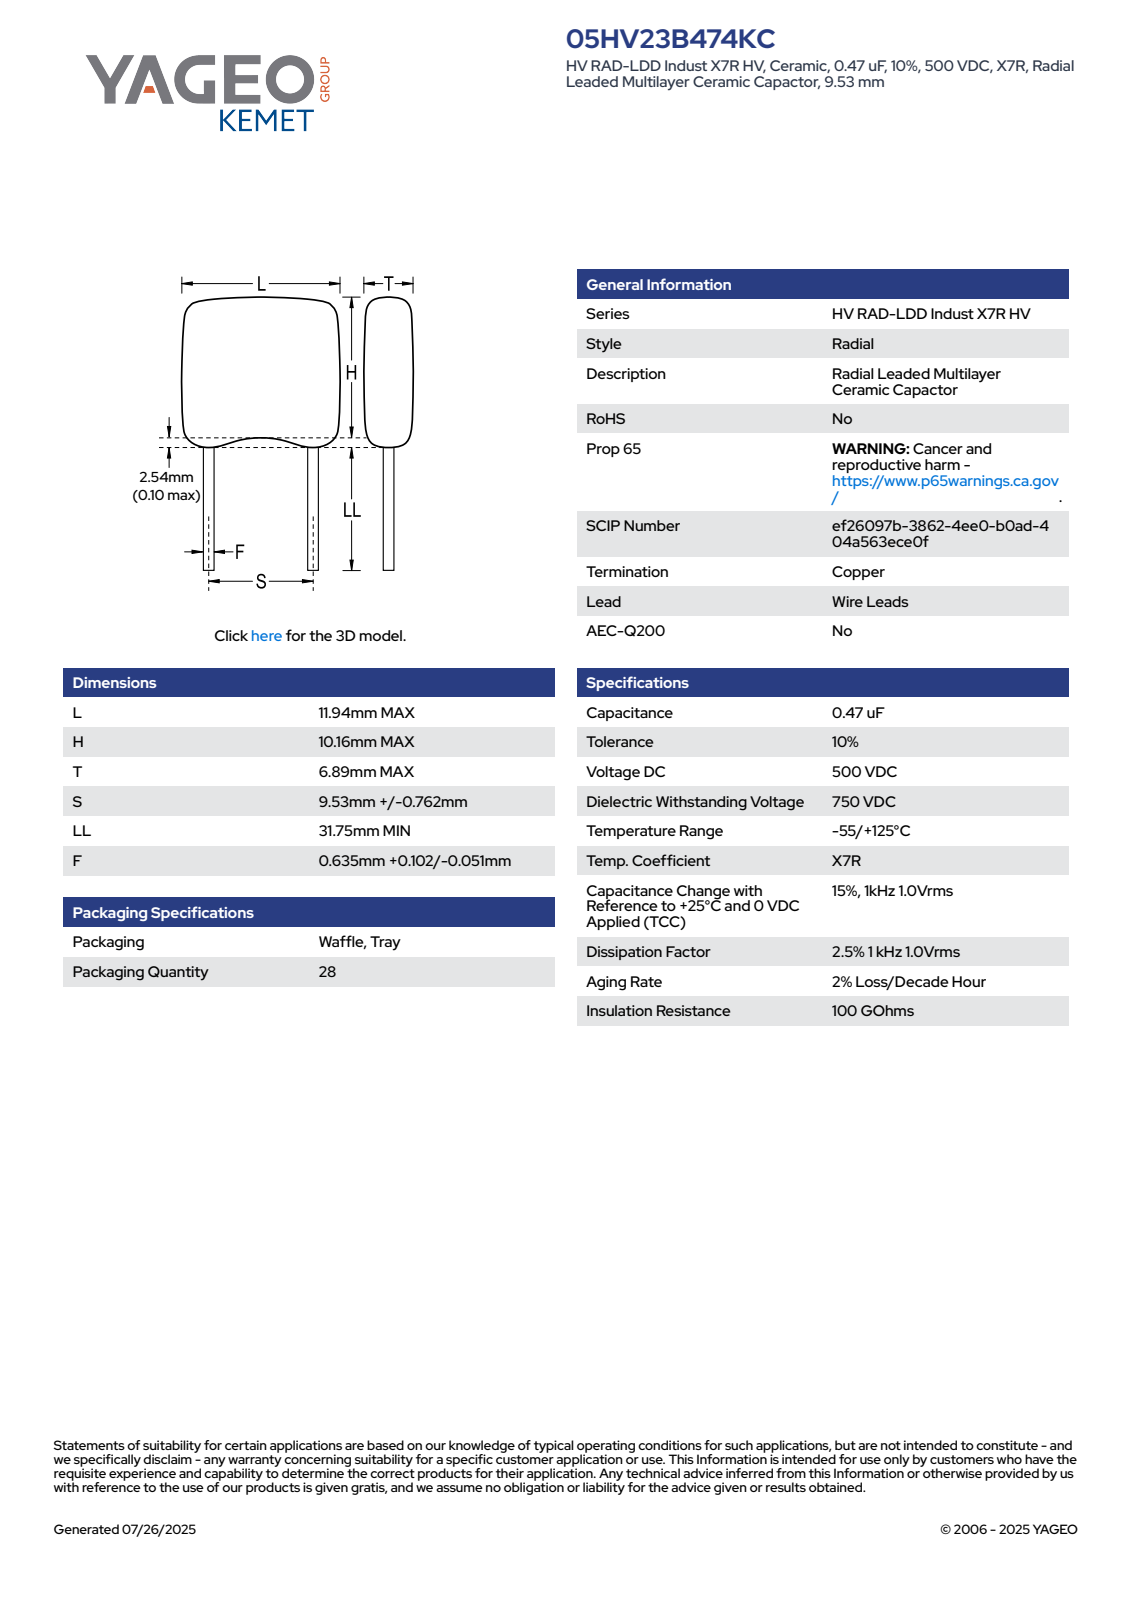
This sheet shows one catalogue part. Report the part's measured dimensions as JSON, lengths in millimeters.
{"part_name": "CCRM_RCST_HV23_L11.94H10.16T6.89S9.53LL31.75F0.737", "step_written_by": "SolidWorks 2021 (AUTOMOTIVE_DESIGN)", "units": "millimeters", "bodies": {"solids": 4, "faces": 98, "planar": 66, "cylindrical": 20, "other": 12}, "overall_size": [14.91, 11.94, 6.89], "volume_mm3": 872, "surface_area_mm2": 577, "round_bosses_or_shafts": [[0.74, 2]], "partial_cylinders_radius": [[1, 8], [0.5, 4]], "face_to_face_distances": [6.89, 11.94, 11.74, 3.17, 14.91, 1.52, 9.89, 6.72, 5.02, 8.37]}
